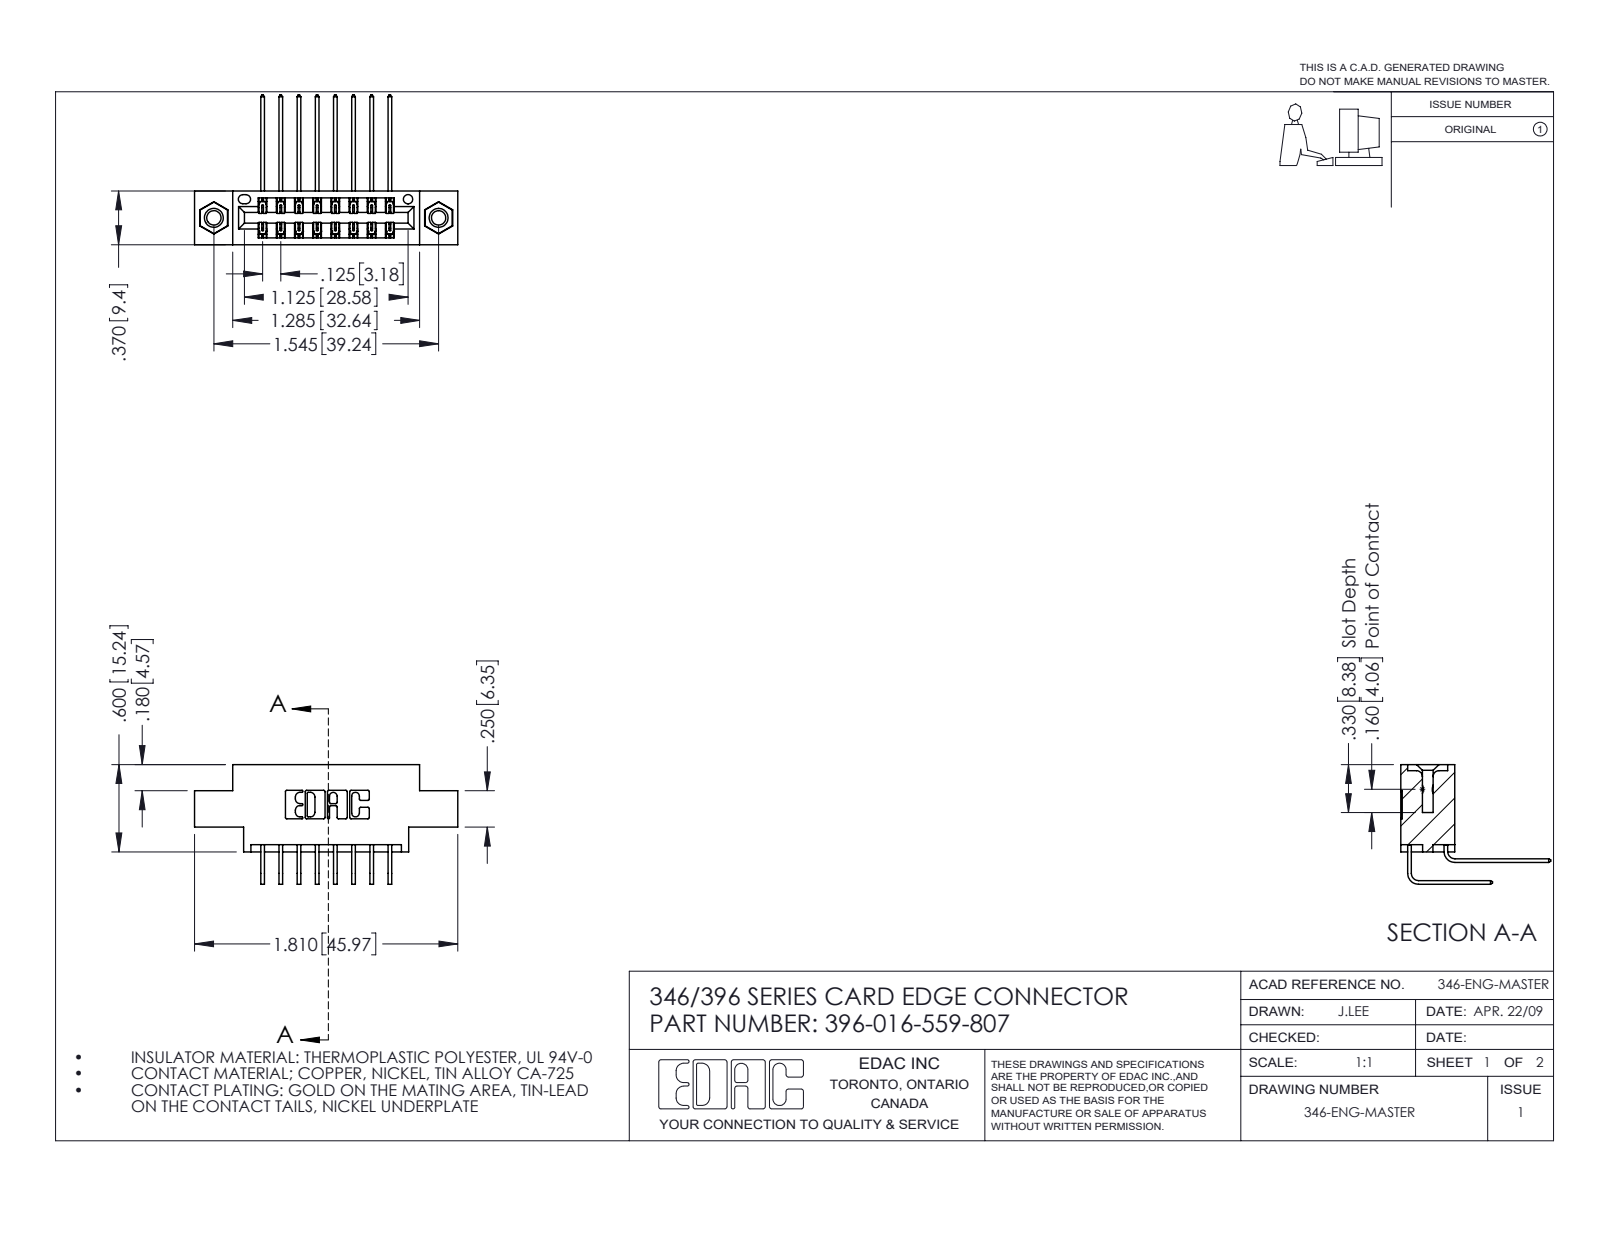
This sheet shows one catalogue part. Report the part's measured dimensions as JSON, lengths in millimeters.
{"part_name": "345-292-001_558 559 Tail - 1; 345-250-001_345-250-005-103; 345-292-001_559 Tail - 2; 396-016-559-807 (+1 more)", "step_written_by": "SolidWorks 2016 (CONFIG_CONTROL_DESIGN)", "units": "millimeters", "bodies": {"solids": 19, "faces": 1050, "planar": 704, "cylindrical": 330, "other": 16}, "overall_size": [46, 26.2, 20.9], "volume_mm3": 4150, "surface_area_mm2": 5817, "round_holes": [[2.5, 2], [3.2, 2], [4, 2], [1.6, 1]], "round_bosses_or_shafts": [[3.9, 2]], "partial_cylinders_radius": [[0.2, 24], [0.3, 22], [0.2, 6], [0.8, 6], [0.7, 3], [0.4, 2], [0.6, 2], [0.6, 2]], "face_to_face_distances": [6.4, 1.2, 9.4, 8.2, 0.6, 1.8, 5.6, 7.6, 3.8, 2.5], "hole_center_spacings": [6.2, 34.1, 39.2]}
